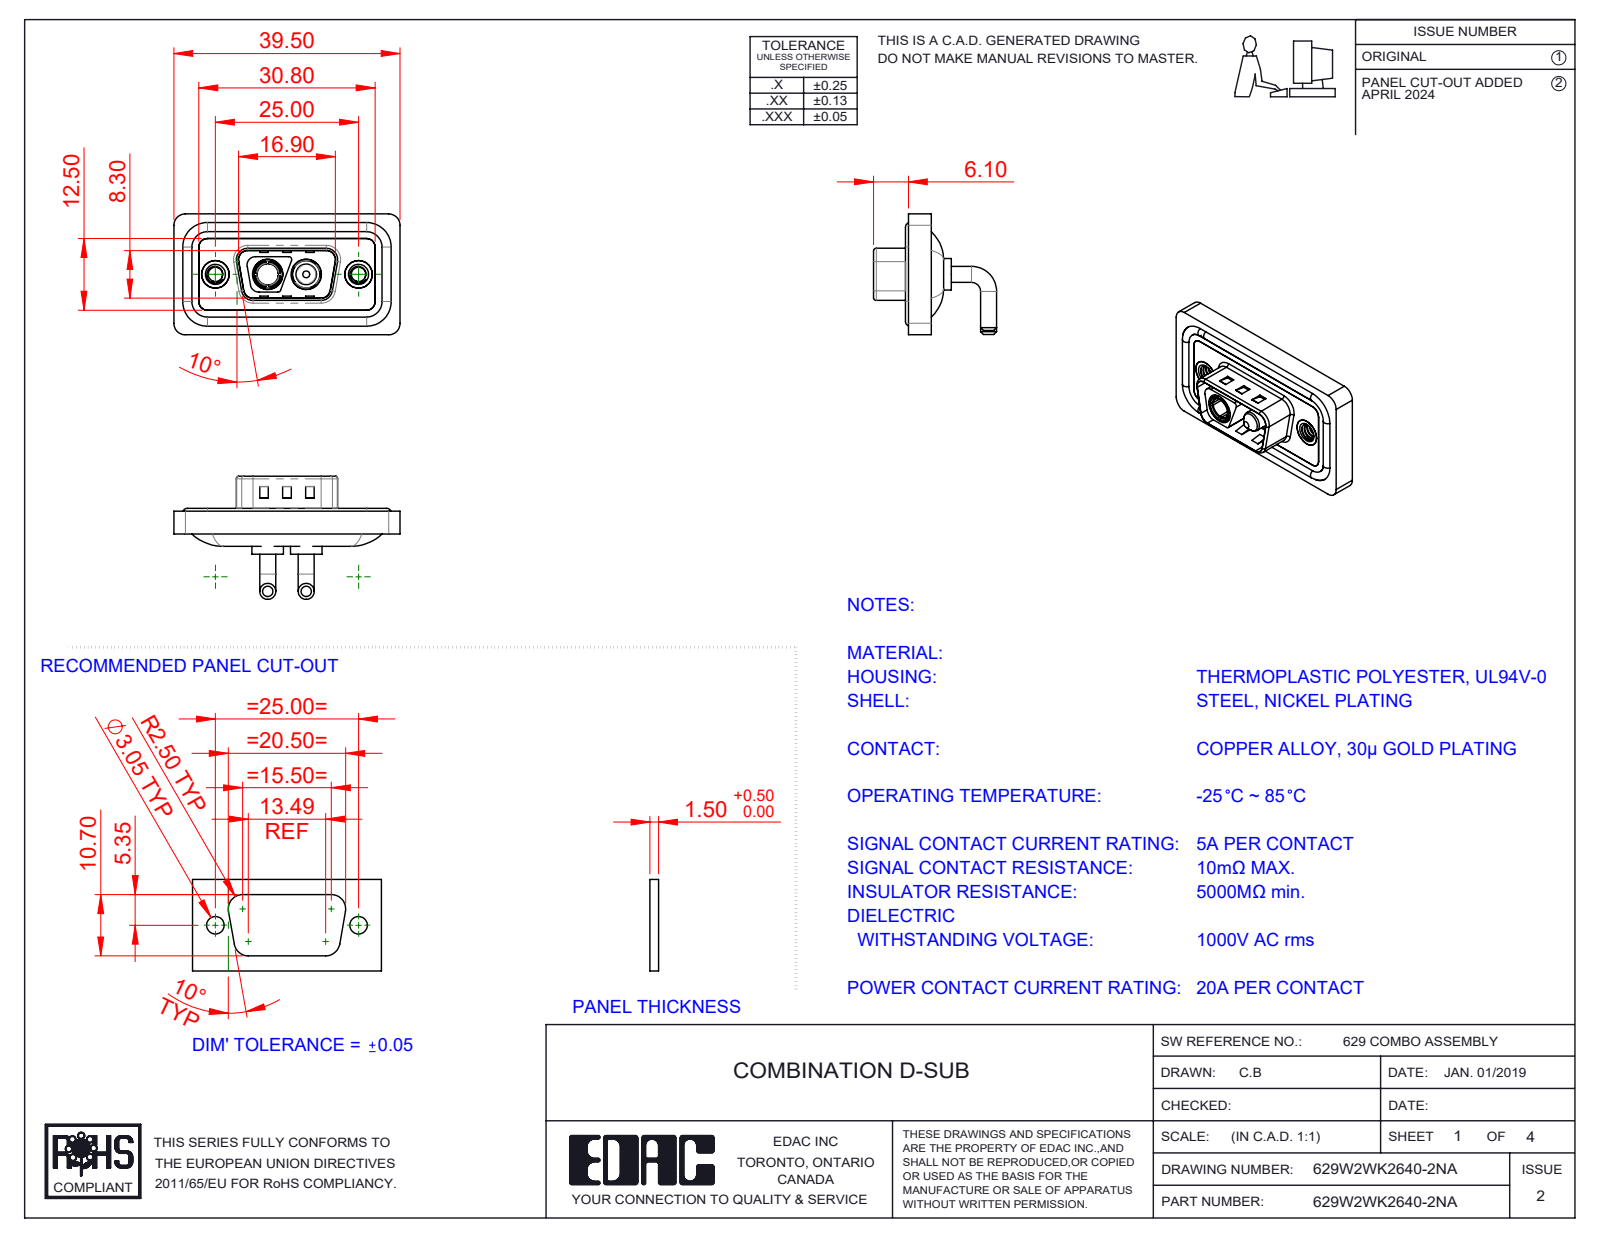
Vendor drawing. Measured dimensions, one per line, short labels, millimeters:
name: 629W2WK2640-2NA; Power Socket_20A RA; Power Pin_20A RA; 629Combo Housing_2WK2 (+4 more)
written by: SolidWorks 2023 (CONFIG_CONTROL_DESIGN)
unit: mm
bodies: 11 solids, 536 faces (189 planar, 229 cylindrical, 118 other)
size: 39.5 × 21.5 × 21.1
volume: 4 686 mm³; area: 7 536 mm²
holes: 2× ⌀2.5, 2× ⌀4, 2× ⌀4.8, 2× ⌀4.85, 2× ⌀5, 2× ⌀5.3, 1× ⌀3.7
bosses: 4× ⌀2.8, 4× ⌀1.6, 2× ⌀5.5, 2× ⌀5.2, 2× ⌀4.9, 2× ⌀4.75, 2× ⌀3.75, 1× ⌀4.96
rounds: 20× R1.5, 18× R2, 10× R0.5, 8× R1.6, 4× R0.25, 4× R0.6, 4× R0.65, 4× R0.9
face distances: 0.4, 2.9, 1.1, 0.8, 2.1, 2.5, 3.1, 1.6, 4.5, 1.5
hole spacings: 9.14, 15.86, 6.72, 25
